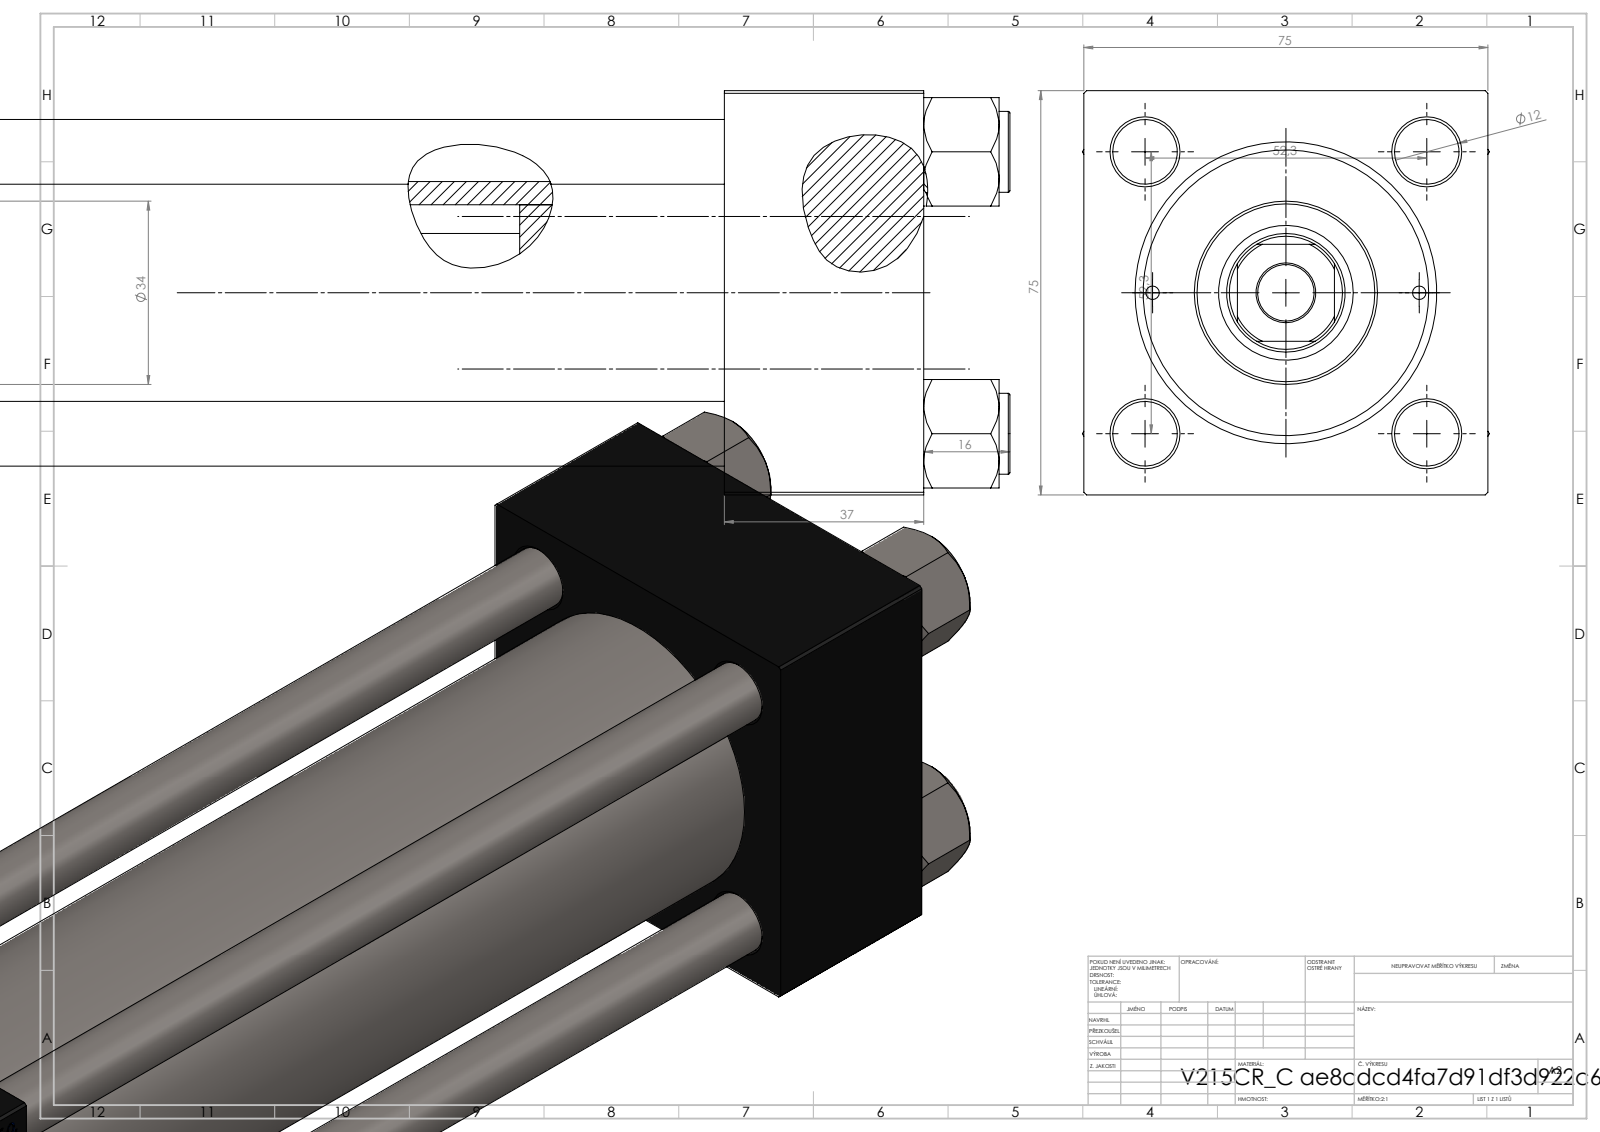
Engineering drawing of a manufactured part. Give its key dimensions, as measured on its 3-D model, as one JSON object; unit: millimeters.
{"part_name": "NUT_M5_C; V215CR_C_Body; V215_VC_A; V215CR_C_TYCINKA (+1 more)", "step_written_by": "SolidWorks 2019 (CONFIG_CONTROL_DESIGN)", "units": "millimeters", "bodies": {"solids": 11, "faces": 1155, "planar": 528, "cylindrical": 91, "other": 536}, "overall_size": [335, 75.54, 75], "volume_mm3": 843308, "surface_area_mm2": 224774, "round_holes": [[12, 4], [2.5, 2], [7, 2], [20.96, 2], [30, 2], [10.5, 1], [22, 1], [25, 1], [41, 1], [50, 1], [53, 1]], "round_bosses_or_shafts": [[15, 4], [56, 1], [34, 1]], "partial_cylinders_radius": [[10.5, 1]], "face_to_face_distances": [75, 37, 294, 257, 235, 198, 59, 265.3, 228.3, 30.3], "hole_center_spacings": [26.19, 36.98, 52.3, 57.22, 24.75, 73.96, 49.5, 233.5]}
